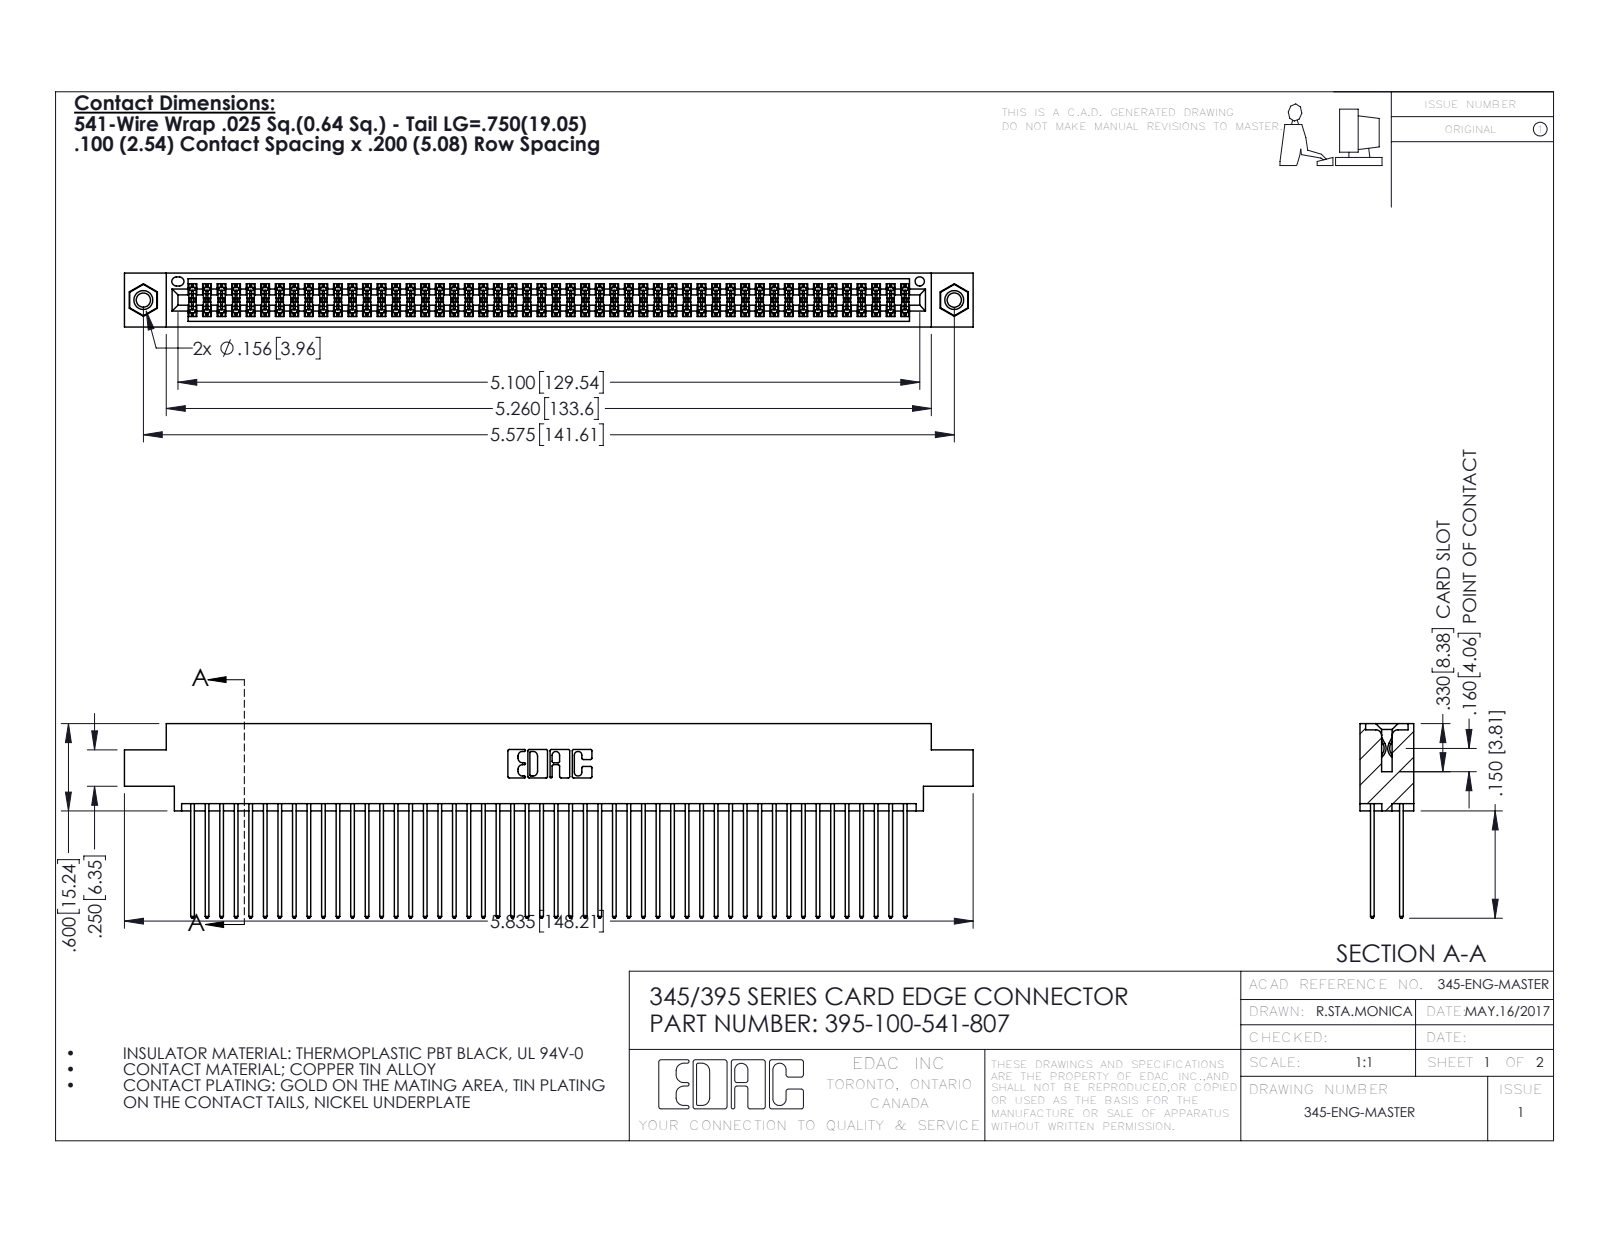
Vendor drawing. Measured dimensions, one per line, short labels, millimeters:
name: 345-292-001_345-293-141; 395-100-541-807; 345 Part_0.170 Offset - 0.156 Dia-TI; 345-250-001_345-250-005-103
written by: SolidWorks 2016 (CONFIG_CONTROL_DESIGN)
unit: mm
bodies: 103 solids, 5190 faces (3416 planar, 1758 cylindrical, 16 other)
size: 148.2 × 34 × 9.4
volume: 14 900 mm³; area: 25 080 mm²
holes: 2× ⌀2.5, 2× ⌀3.2, 2× ⌀4, 1× ⌀1.6
bosses: 2× ⌀3.9
rounds: 150× R0.2, 100× R0.3, 22× R0.3, 6× R0.2, 6× R0.8, 3× R0.7, 2× R0.4, 2× R0.5
face distances: 1.8, 7.6, 5.1, 2.5, 6.9, 0.6, 5.7, 9.4, 4.4, 3.8
hole spacings: 6.9, 135.6, 141.6
